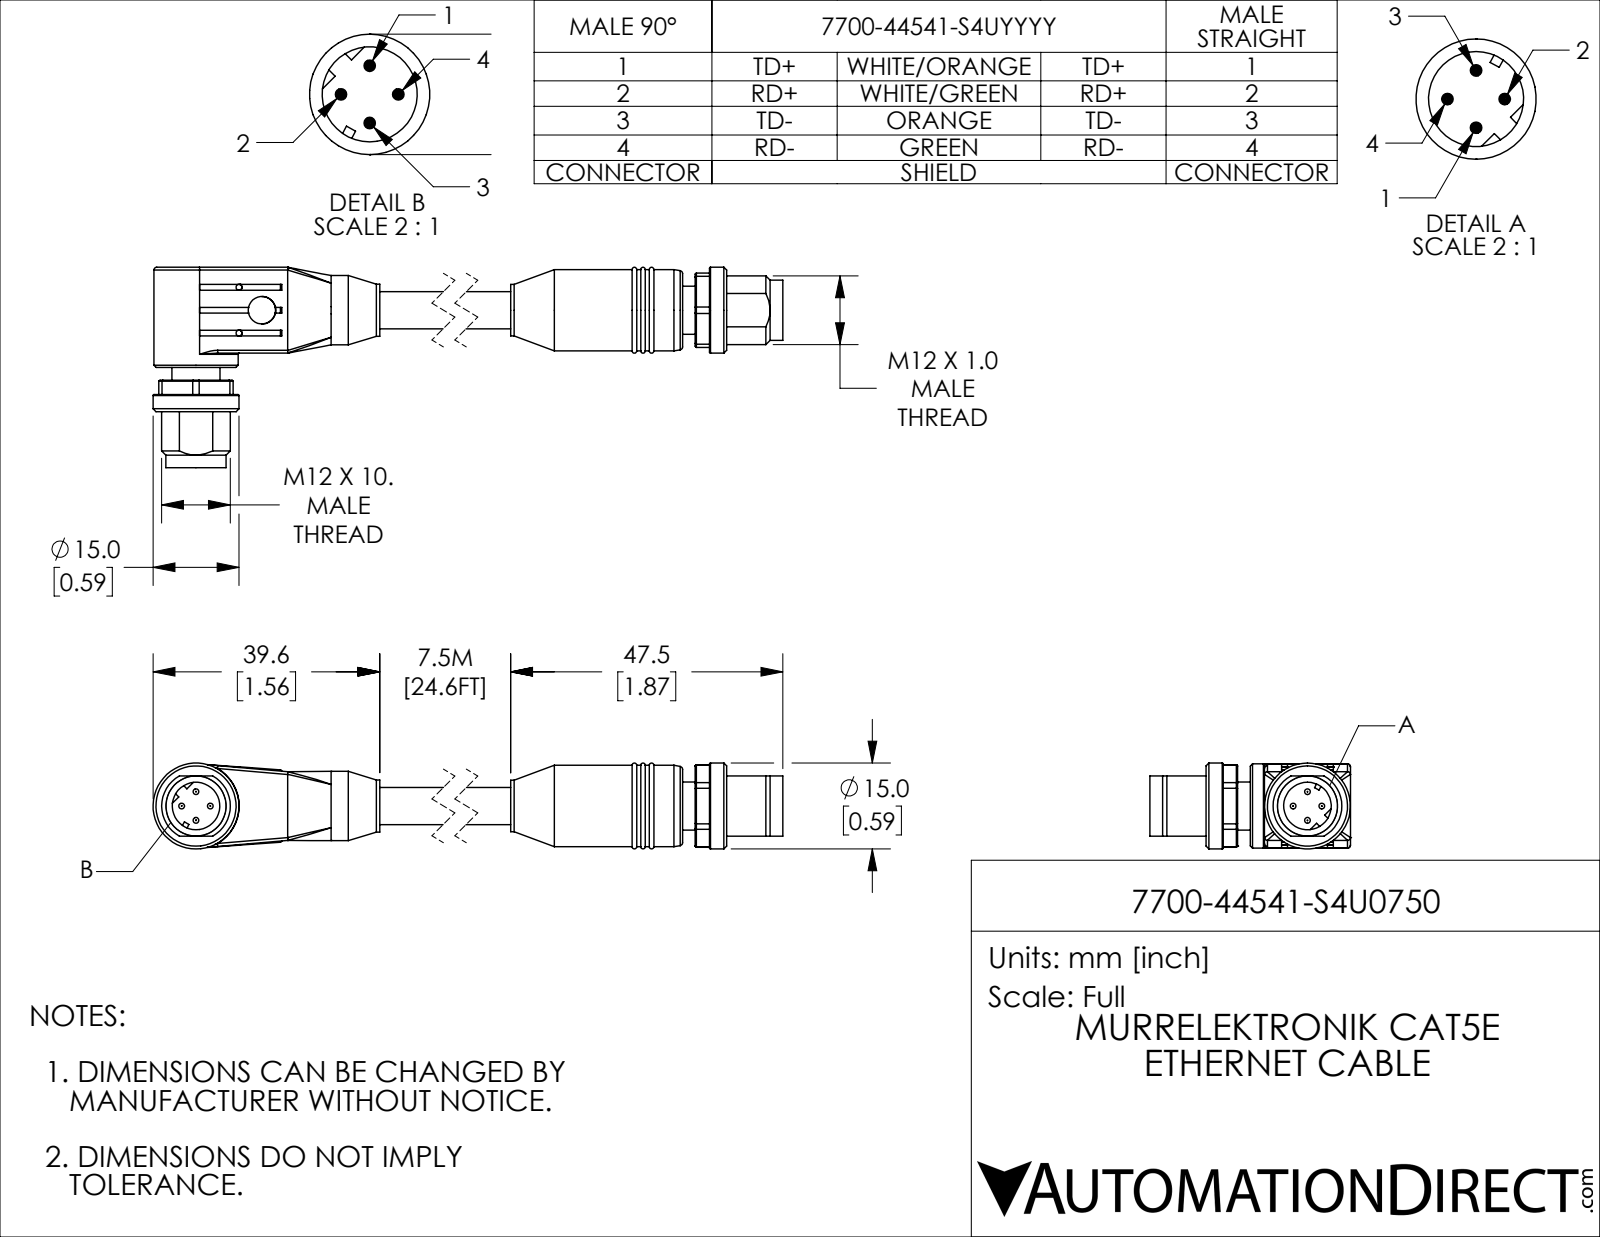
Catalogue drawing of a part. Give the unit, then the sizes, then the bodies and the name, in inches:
Units: inches
Overall size (bounding box): 5.254 × 1.378 × 0.591
Round holes (diameter × count): ⌀0.041 ×4, ⌀0.327 ×2, ⌀0.189 ×1
Round bosses / shafts (diameter × count): ⌀0.039 ×8, ⌀0.591 ×2, ⌀0.413 ×2, ⌀0.331 ×2, ⌀0.579 ×1, ⌀0.559 ×1, ⌀0.476 ×1, ⌀0.358 ×1
Partial cylindrical surfaces — rounded edges, fillets, slot ends (radius × count): R0.02 ×4, R0.012 ×2, R0.236 ×2, R0.283 ×2
Main face-to-face distances: 0.689, 0.087, 0.098, 0.185, 0.591, 0.035, 0.252, 0.339, 0.217, 0.303
Hole centre spacings: 0.315
Volume: 0.955 in³ · Surface area: 10.92 in²
Bodies: 2 solids, 284 faces (114 planar, 90 cylindrical, 80 other)
Part name (STEP PRODUCT): 7700-44541-S4U0750; 7700-44541-S4U0750_2; 7700-44541-S4U0750_1
STEP written by: SolidWorks 2021 (CONFIG_CONTROL_DESIGN)
